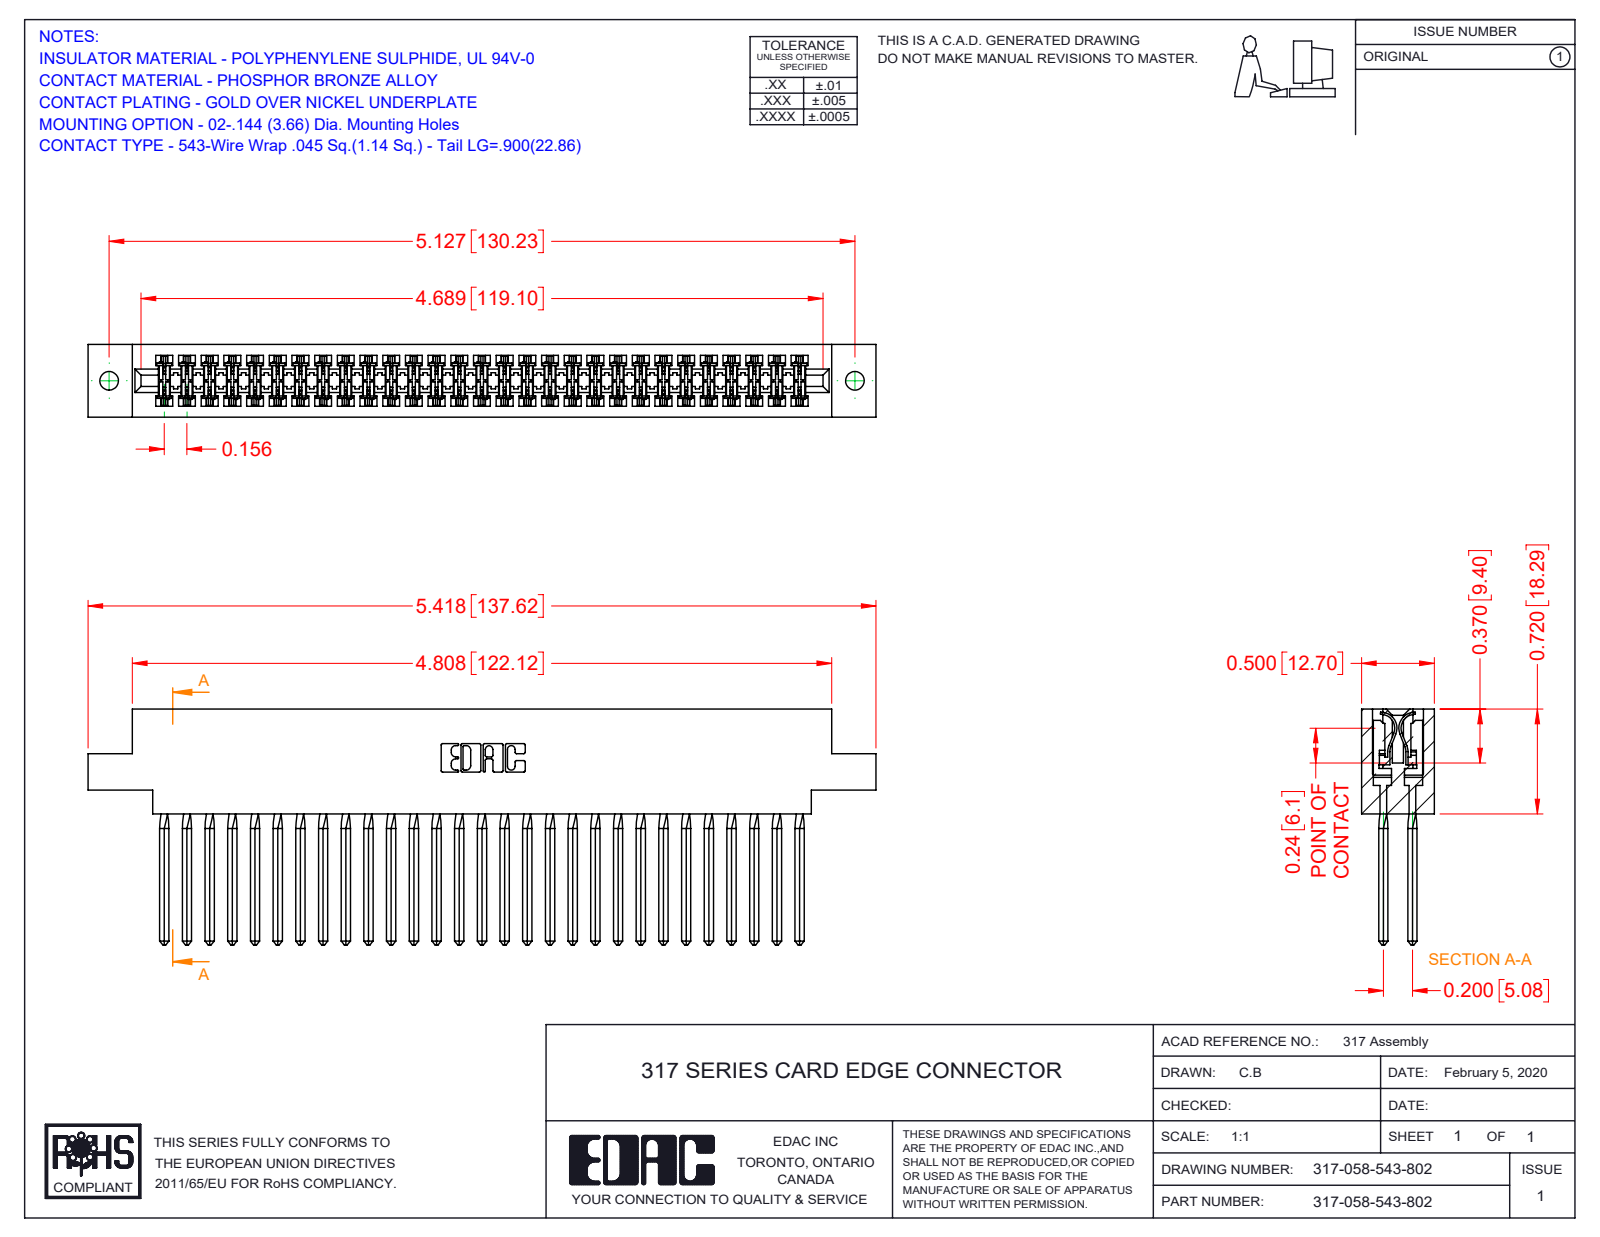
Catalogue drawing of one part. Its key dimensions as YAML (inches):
part_name: "317 Part_.144 Dia; 317-290-001_543; 317-058-543-802"
step_written_by: "SolidWorks 2016 (CONFIG_CONTROL_DESIGN)"
units: inches
bodies: {solids: 59, faces: 5264, planar: 4292, cylindrical: 740, other: 232}
overall_size: [5.418, 1.62, 0.5]
volume: 1.398
surface_area: 52.67
round_holes:
  - {diameter: 0.128, count: 2}
partial_cylinders:
  - {radius: 0.015, count: 116}
  - {radius: 0.01, count: 22}
  - {radius: 0.007, count: 6}
  - {radius: 0.031, count: 6}
  - {radius: 0.026, count: 3}
  - {radius: 0.095, count: 2}
  - {radius: 0.1, count: 2}
  - {radius: 0.11, count: 2}
face_to_face_distances: [0.5, 0.075, 0.425, 0.35, 0.11, 0.195, 0.094, 0.2, 0.72, 0.115]
hole_center_spacings: [5.127]
